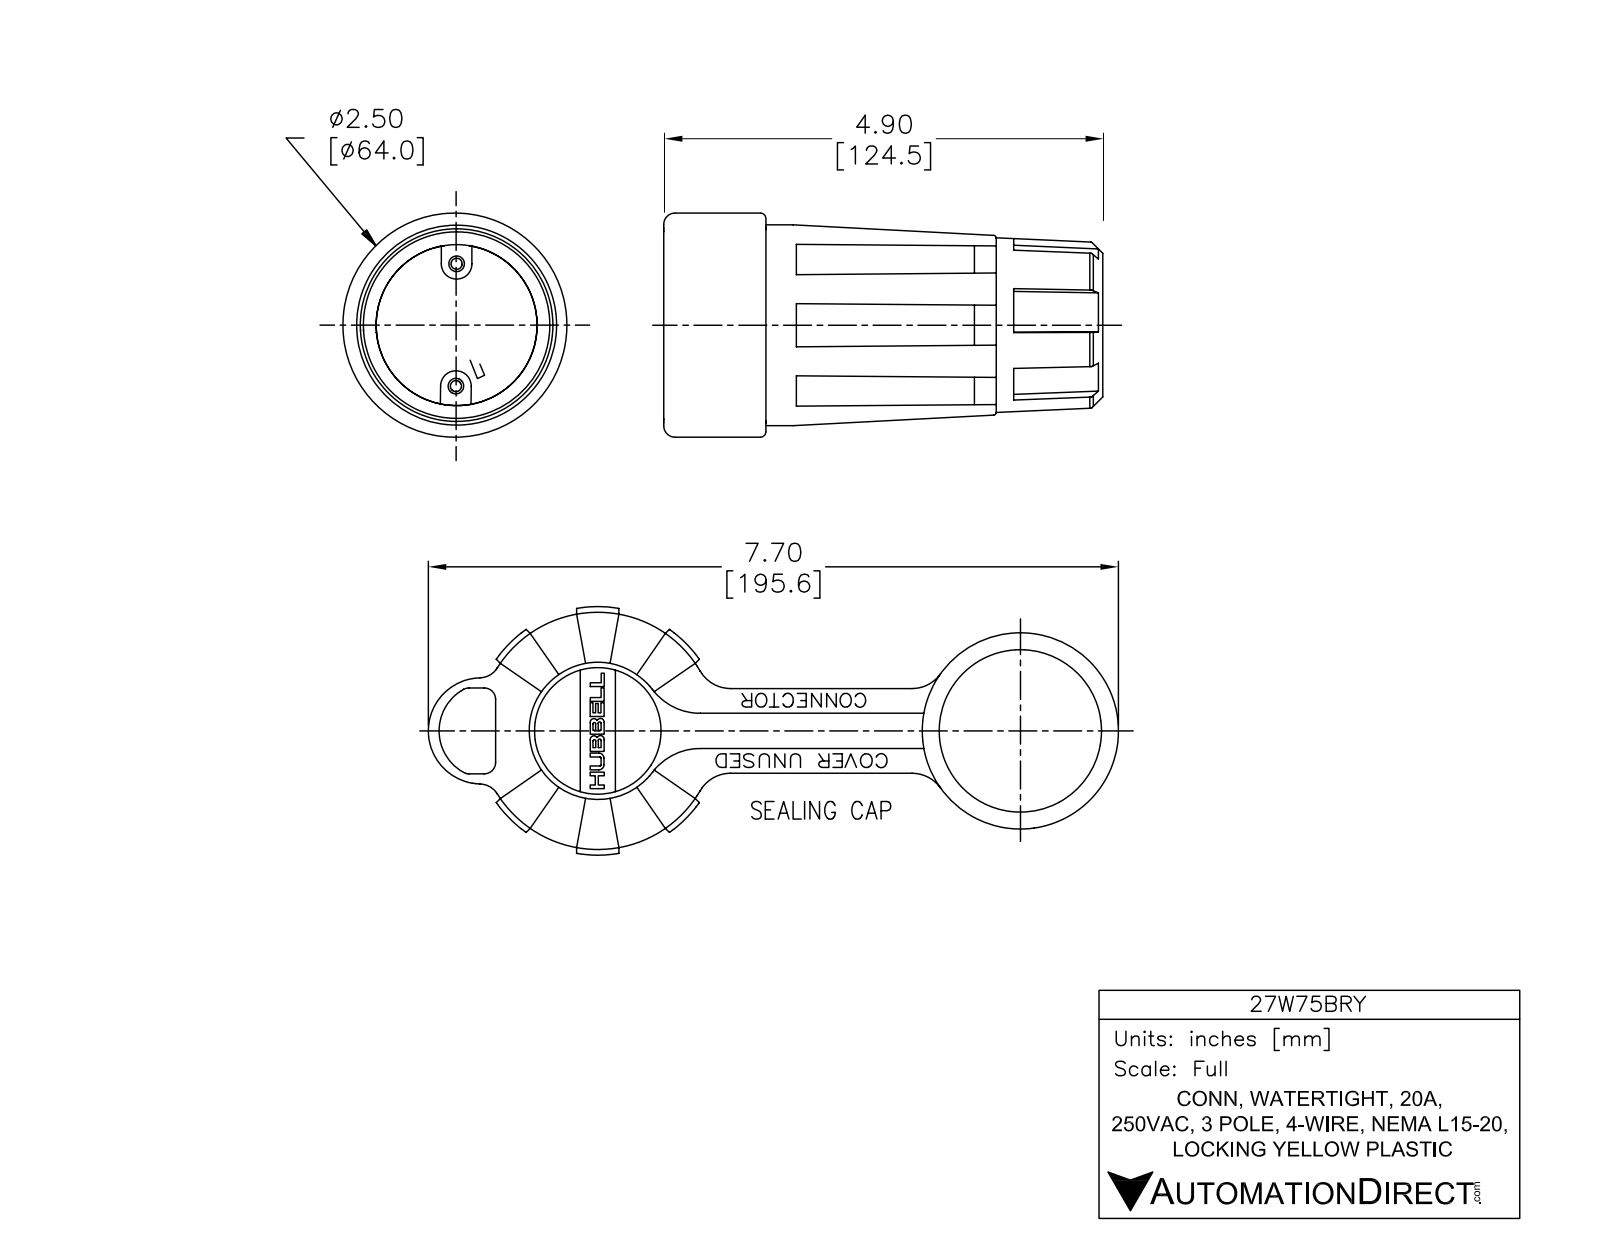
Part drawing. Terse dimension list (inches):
name: 27W75BRY
written by: SolidWorks 2013 (AUTOMOTIVE_DESIGN)
unit: in
bodies: 1 solid, 359 faces (137 planar, 98 cylindrical, 124 other)
size: 8.08 × 4.966 × 3.139
volume: 20.16 in³; area: 104.7 in²
holes: 1× ⌀0.95, 1× ⌀1.82, 1× ⌀1.86, 1× ⌀2.345, 1× ⌀2.805
bosses: 2× ⌀0.2, 1× ⌀2.76, 1× ⌀2.755, 1× ⌀2.43, 1× ⌀2.25, 1× ⌀1.975, 1× ⌀1.415
rounds: 16× R0.015, 8× R0.061, 6× R0.25, 6× R1.57, 2× R0.1, 2× R0.11, 1× R0.4, 1× R0.402
face distances: 0.08, 0.38, 0.67, 0.75, 0.06, 0.81, 0.14, 0.13, 2.685, 2.555
hole spacings: 4.7
